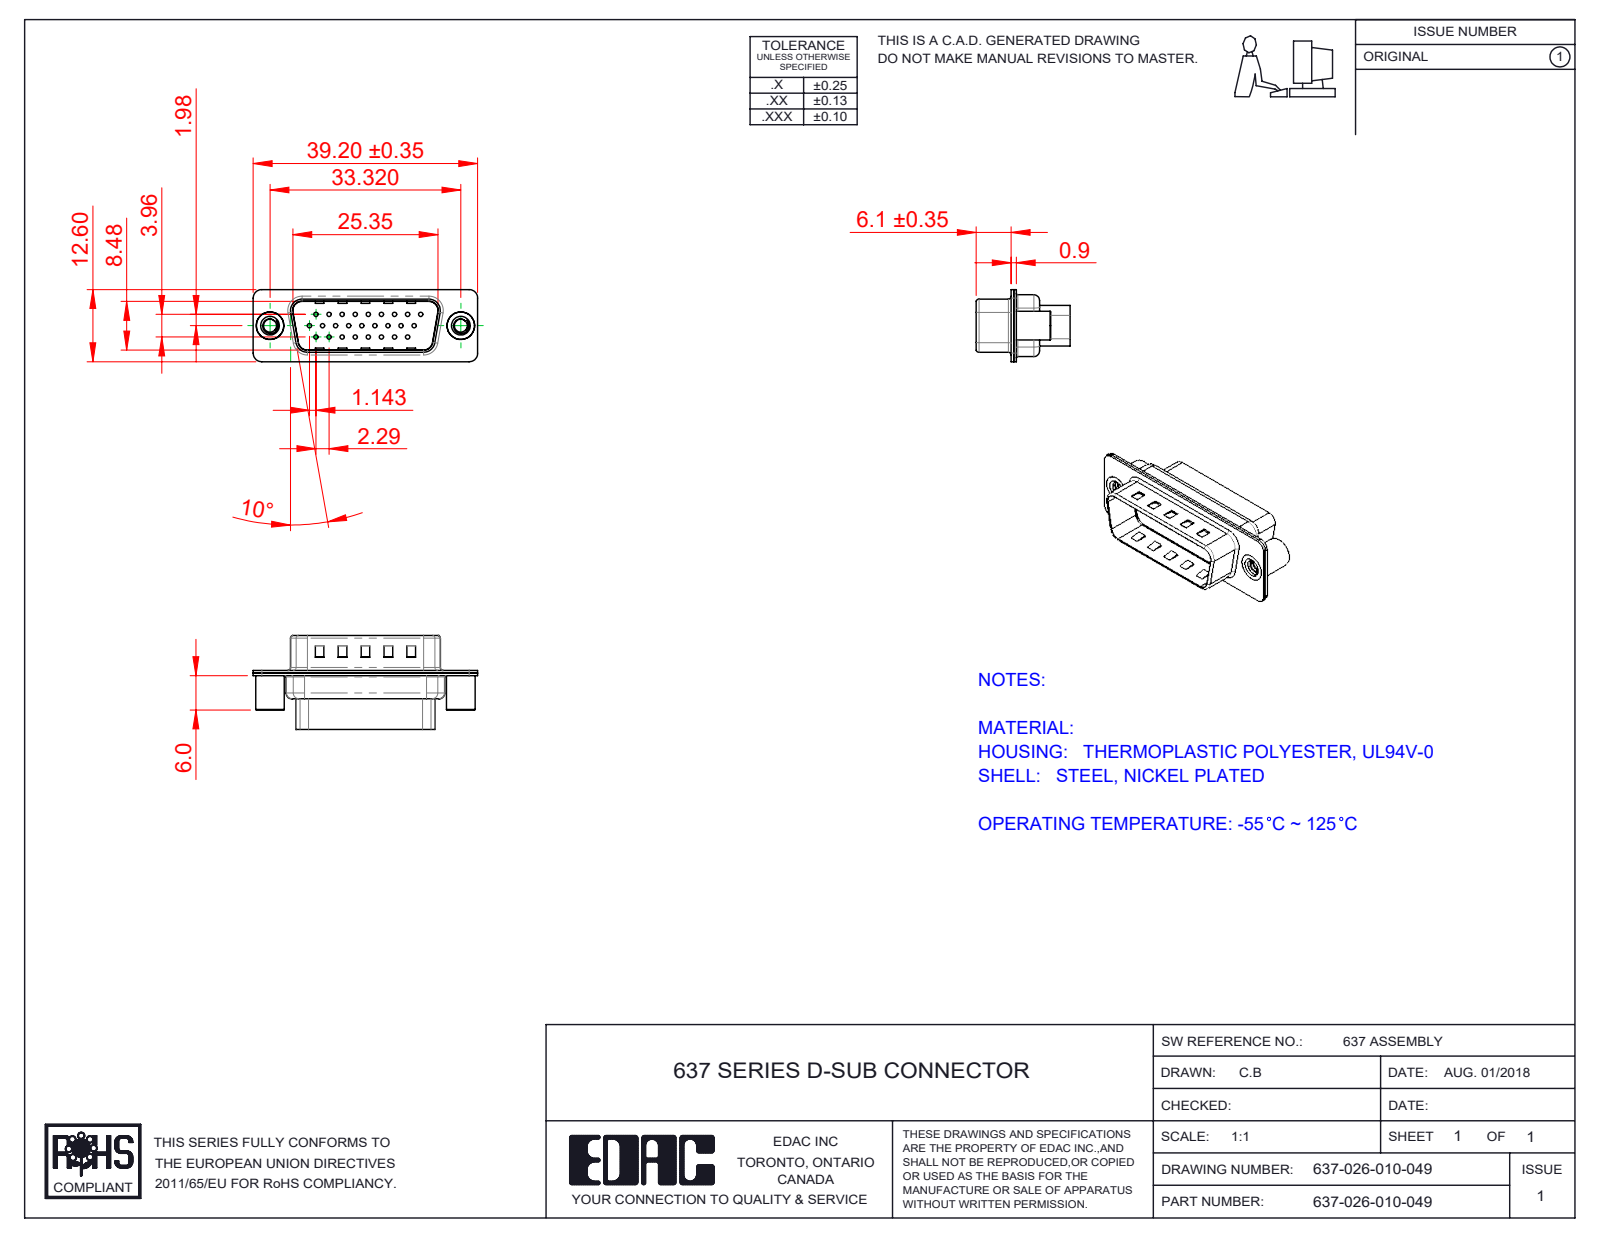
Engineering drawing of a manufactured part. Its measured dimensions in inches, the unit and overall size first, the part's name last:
Units: inches
Overall size (bounding box): 1.543 × 0.646 × 0.496
Round holes (diameter × count): ⌀0.03 ×26, ⌀0.063 ×26, ⌀0.079 ×26, ⌀0.089 ×2, ⌀0.157 ×2, ⌀0.189 ×2
Round bosses / shafts (diameter × count): ⌀0.197 ×2, ⌀0.193 ×2
Partial cylindrical surfaces — rounded edges, fillets, slot ends (radius × count): R0.059 ×16, R0.079 ×12, R0.02 ×8, R0.01 ×4, R0.022 ×4, R0.028 ×4, R0.037 ×4, R0.039 ×4
Main face-to-face distances: 0.018, 0.028, 0.016, 0.035, 0.306, 0.334, 0.043, 0.322, 0.35, 0.012
Hole centre spacings: 0.156, 0.09, 0.18, 0.238, 0.09, 0.324, 0.27, 0.413
Volume: 0.131 in³ · Surface area: 8.231 in²
Bodies: 5 solids, 570 faces (191 planar, 309 cylindrical, 70 other)
Part name (STEP PRODUCT): 637 Shell Rear_26 Contacts; 637 Housing_26 Contacts HP; 637-026-010-049; 637 4-40 Threaded Standoff BS (+1 more)
STEP written by: SolidWorks 2020 (CONFIG_CONTROL_DESIGN)
